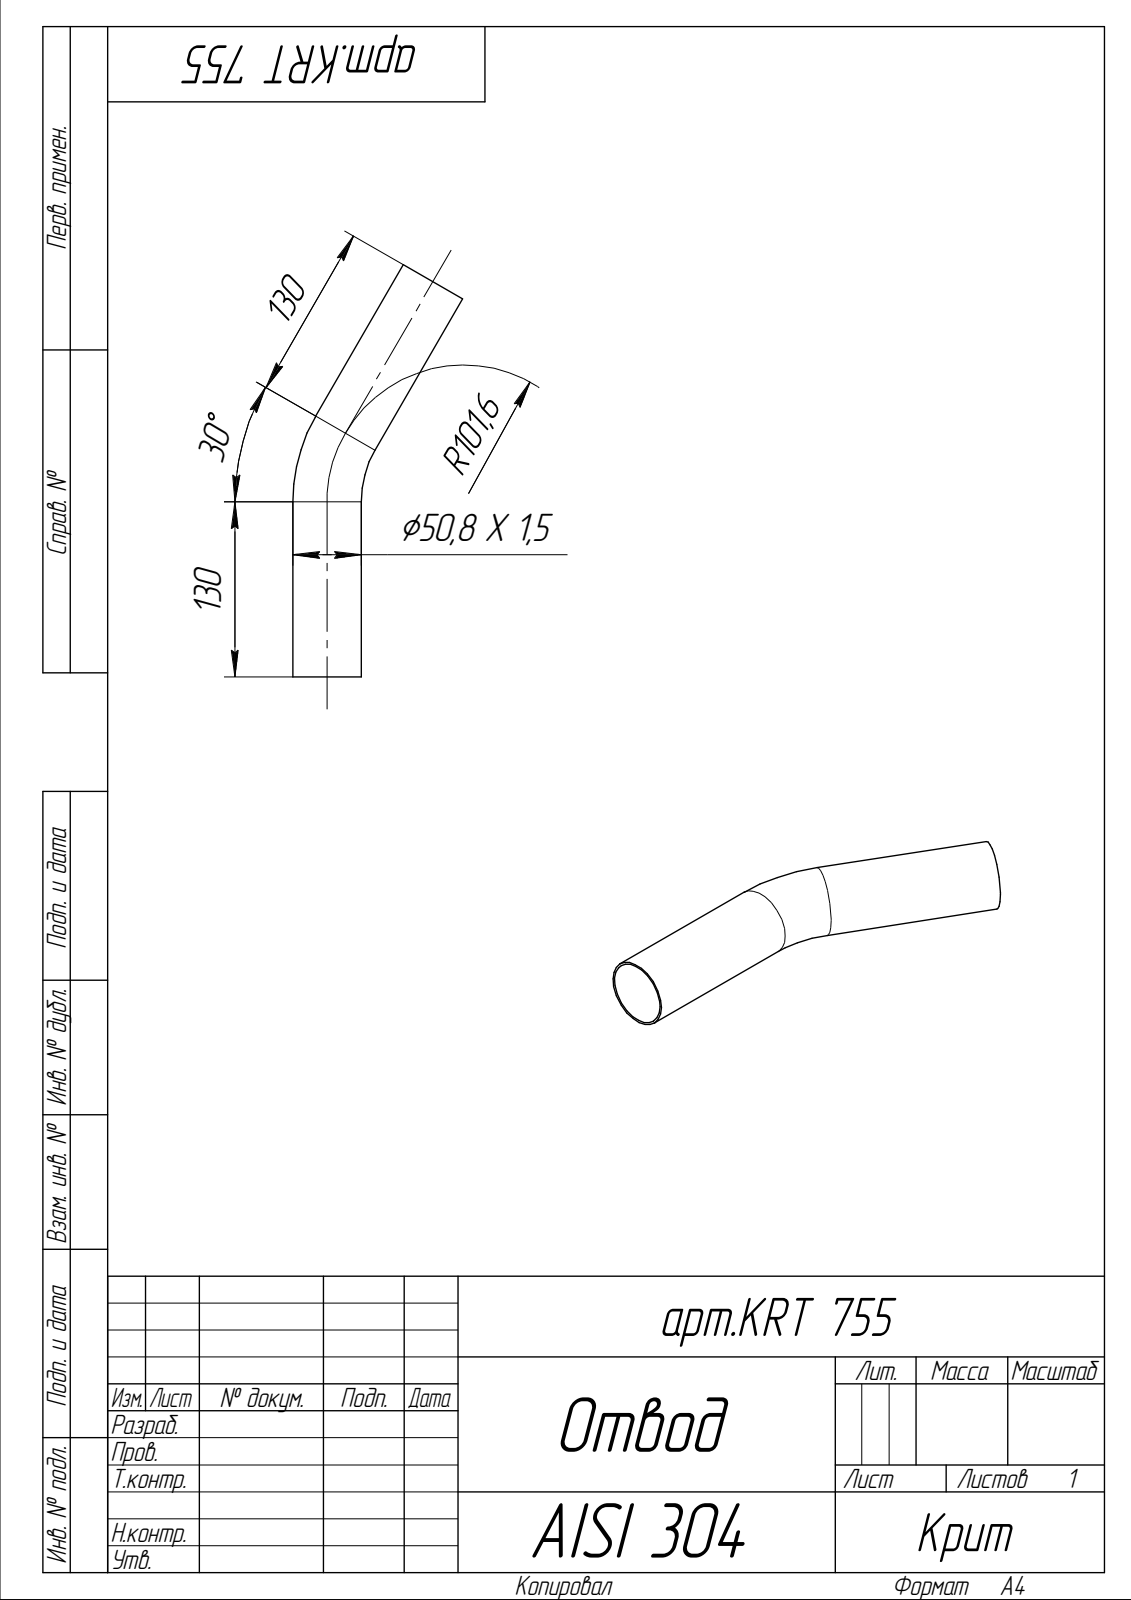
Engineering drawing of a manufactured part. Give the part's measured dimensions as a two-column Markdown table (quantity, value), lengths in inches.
| quantity | value |
| --- | --- |
| part name | Деталь |
| STEP written by | ASCON Math Kernel (AUTOMOTIVE_DESIGN) |
| units | inches |
| bodies | 1 solid, 8 faces (2 planar, 4 cylindrical, 2 other) |
| overall size | 11.22 × 4.452 × 1.669 |
| volume | 4.543 in³ |
| surface area | 116.2 in² |
| round holes (diameter × count) | 1.512 × 2 |
| round bosses / shafts (diameter × count) | 1.669 × 2 |
